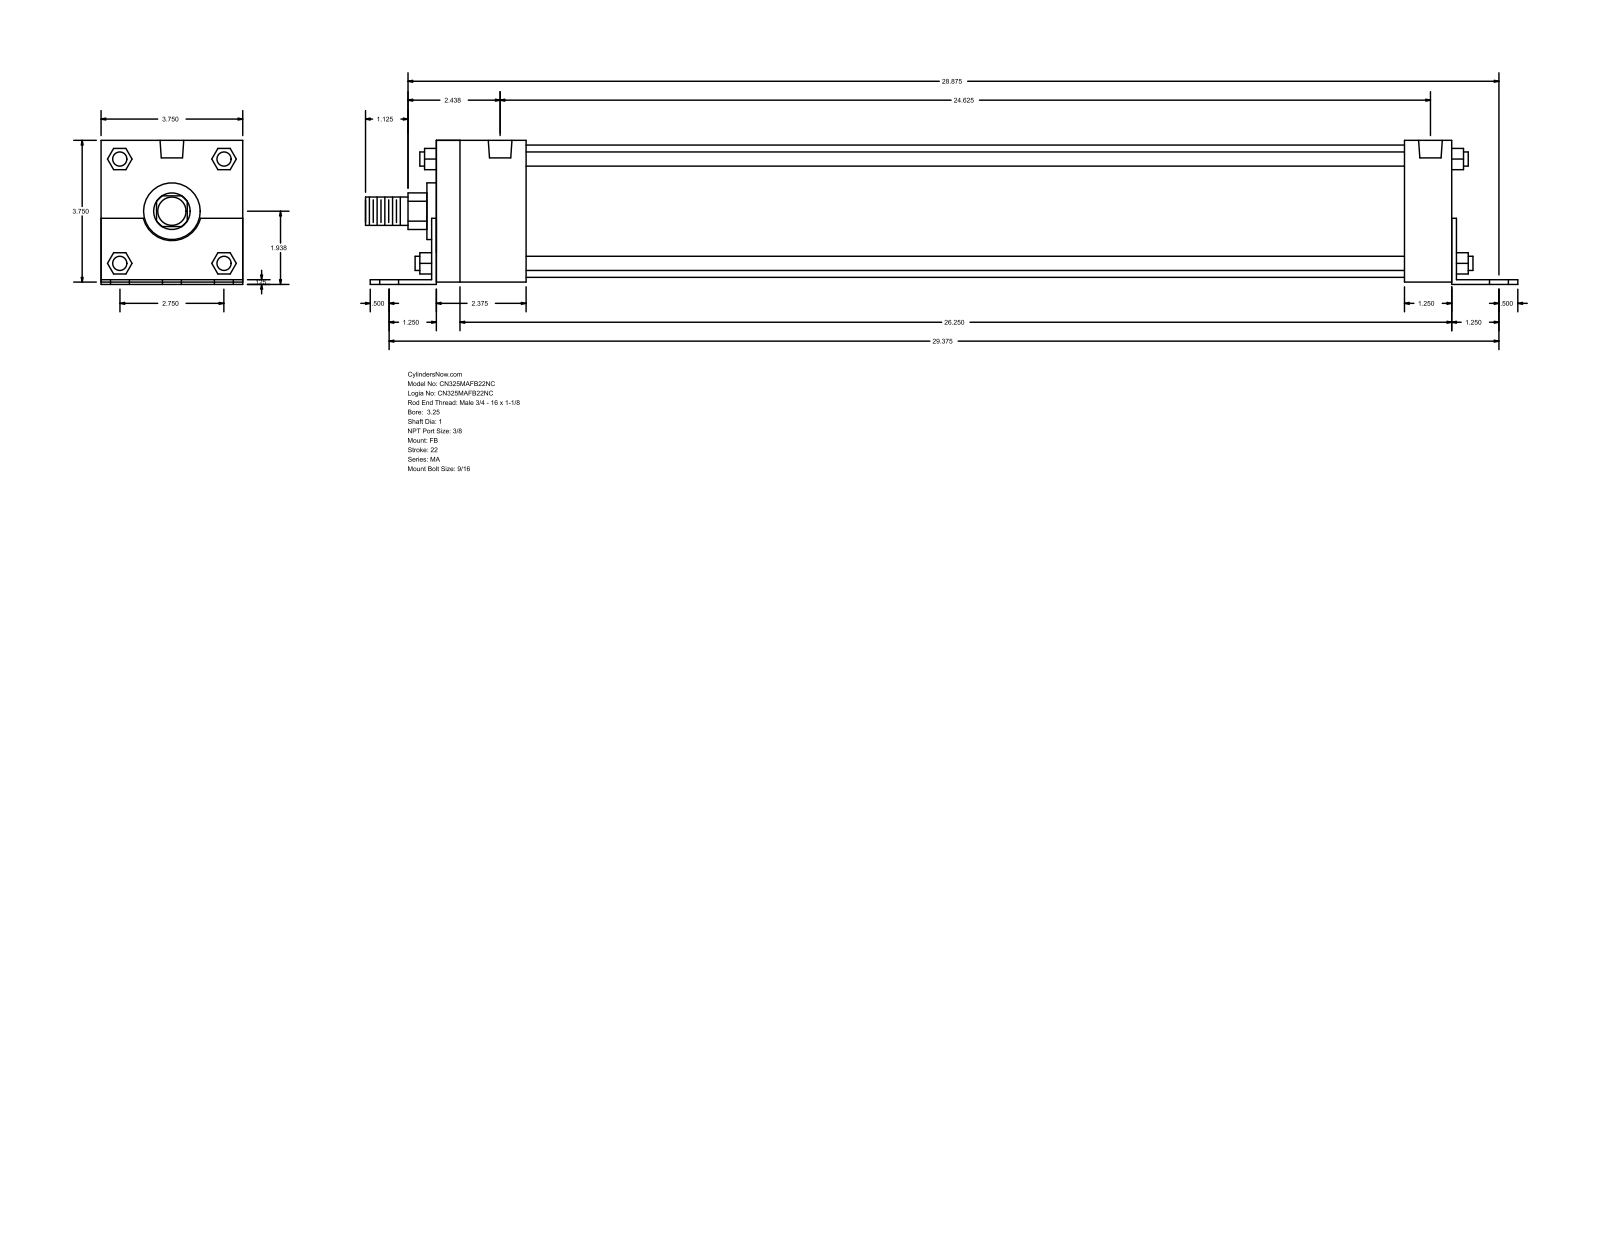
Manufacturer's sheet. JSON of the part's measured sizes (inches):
{"part_name": "MA_FB__0325_1", "step_written_by": "GSSL Pune (CONFIG_CONTROL_DESIGN)", "units": "inches", "bodies": {"solids": 0, "faces": 140, "planar": 105, "cylindrical": 35, "other": 0}, "overall_size": [30.5, 3.813, 3.75], "round_holes": [[0.563, 6], [0.437, 4], [0.627, 2]], "round_bosses_or_shafts": [[0.375, 4], [3.5, 1], [1.5, 1], [1, 1], [0.75, 1]], "partial_cylinders_radius": [[0.484, 1], [0.78, 1]], "face_to_face_distances": [3.75, 0.125, 0.063, 3.812, 0.062, 3.687, 0.125, 26.875, 27.125, 27], "hole_center_spacings": [1.375, 29.407, 29.375, 2.275, 2.427, 2.75, 3.243, 3.414]}
